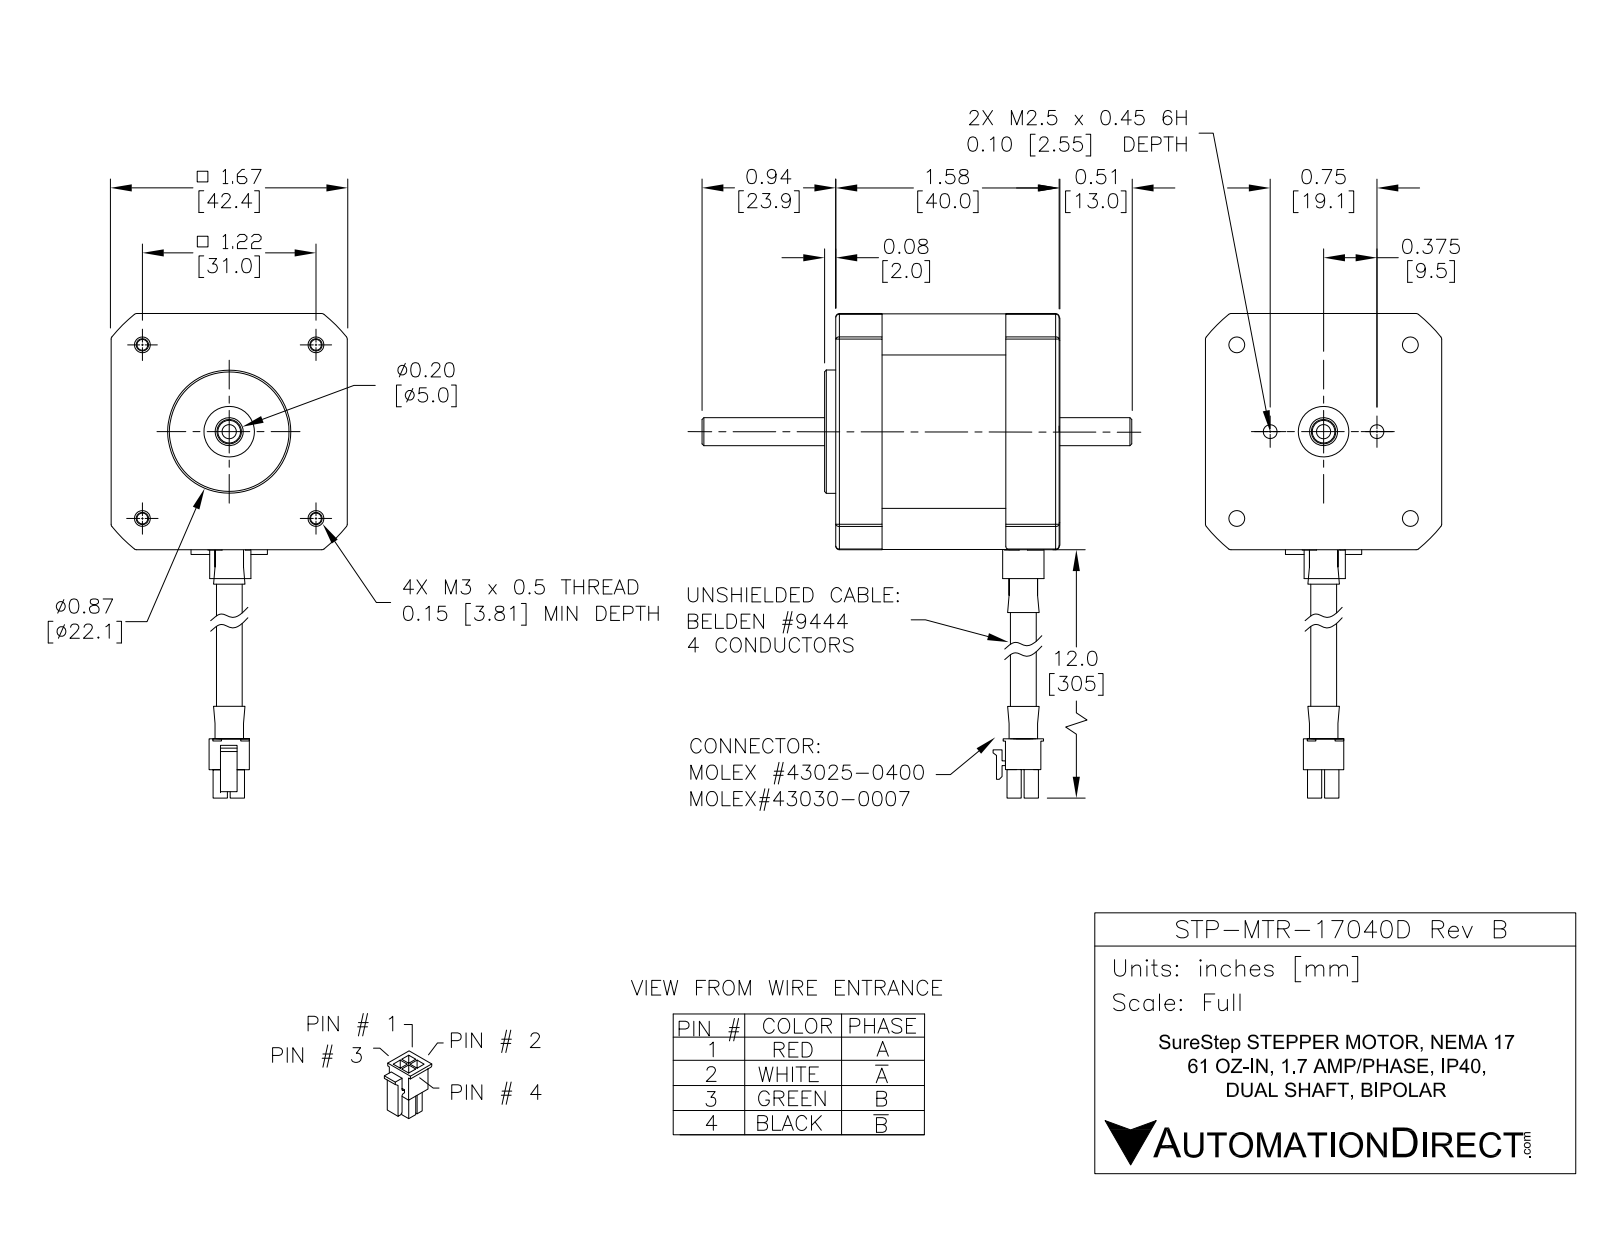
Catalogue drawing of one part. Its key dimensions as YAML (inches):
part_name: "STP-MTR-17040E"
step_written_by: "SolidWorks 2017 (AUTOMOTIVE_DESIGN)"
units: inches
bodies: {solids: 8, faces: 429, planar: 257, cylindrical: 114, other: 58}
overall_size: [13.976, 3.02, 1.66]
volume: 4.702
surface_area: 30.27
round_holes:
  - {diameter: 0.086, count: 4}
  - {diameter: 0.15, count: 4}
  - {diameter: 0.079, count: 2}
  - {diameter: 0.05, count: 1}
  - {diameter: 0.25, count: 1}
  - {diameter: 0.355, count: 1}
round_bosses_or_shafts:
  - {diameter: 0.13, count: 4}
  - {diameter: 0.866, count: 1}
  - {diameter: 0.29, count: 1}
  - {diameter: 0.217, count: 1}
  - {diameter: 0.197, count: 1}
partial_cylinders:
  - {radius: 0.025, count: 17}
  - {radius: 0.012, count: 3}
  - {radius: 0.006, count: 1}
  - {radius: 0.147, count: 1}
  - {radius: 0.986, count: 1}
  - {radius: 0.988, count: 1}
  - {radius: 1.025, count: 1}
  - {radius: 1.06, count: 1}
face_to_face_distances: [1.658, 1.575, 1.656, 1.66, 0.118, 1.654, 0.079, 0.098, 0.089, 0.027]
hole_center_spacings: [1.159, 1.22, 0.863, 0.654, 0.654, 1.726, 0.375, 0.375]
